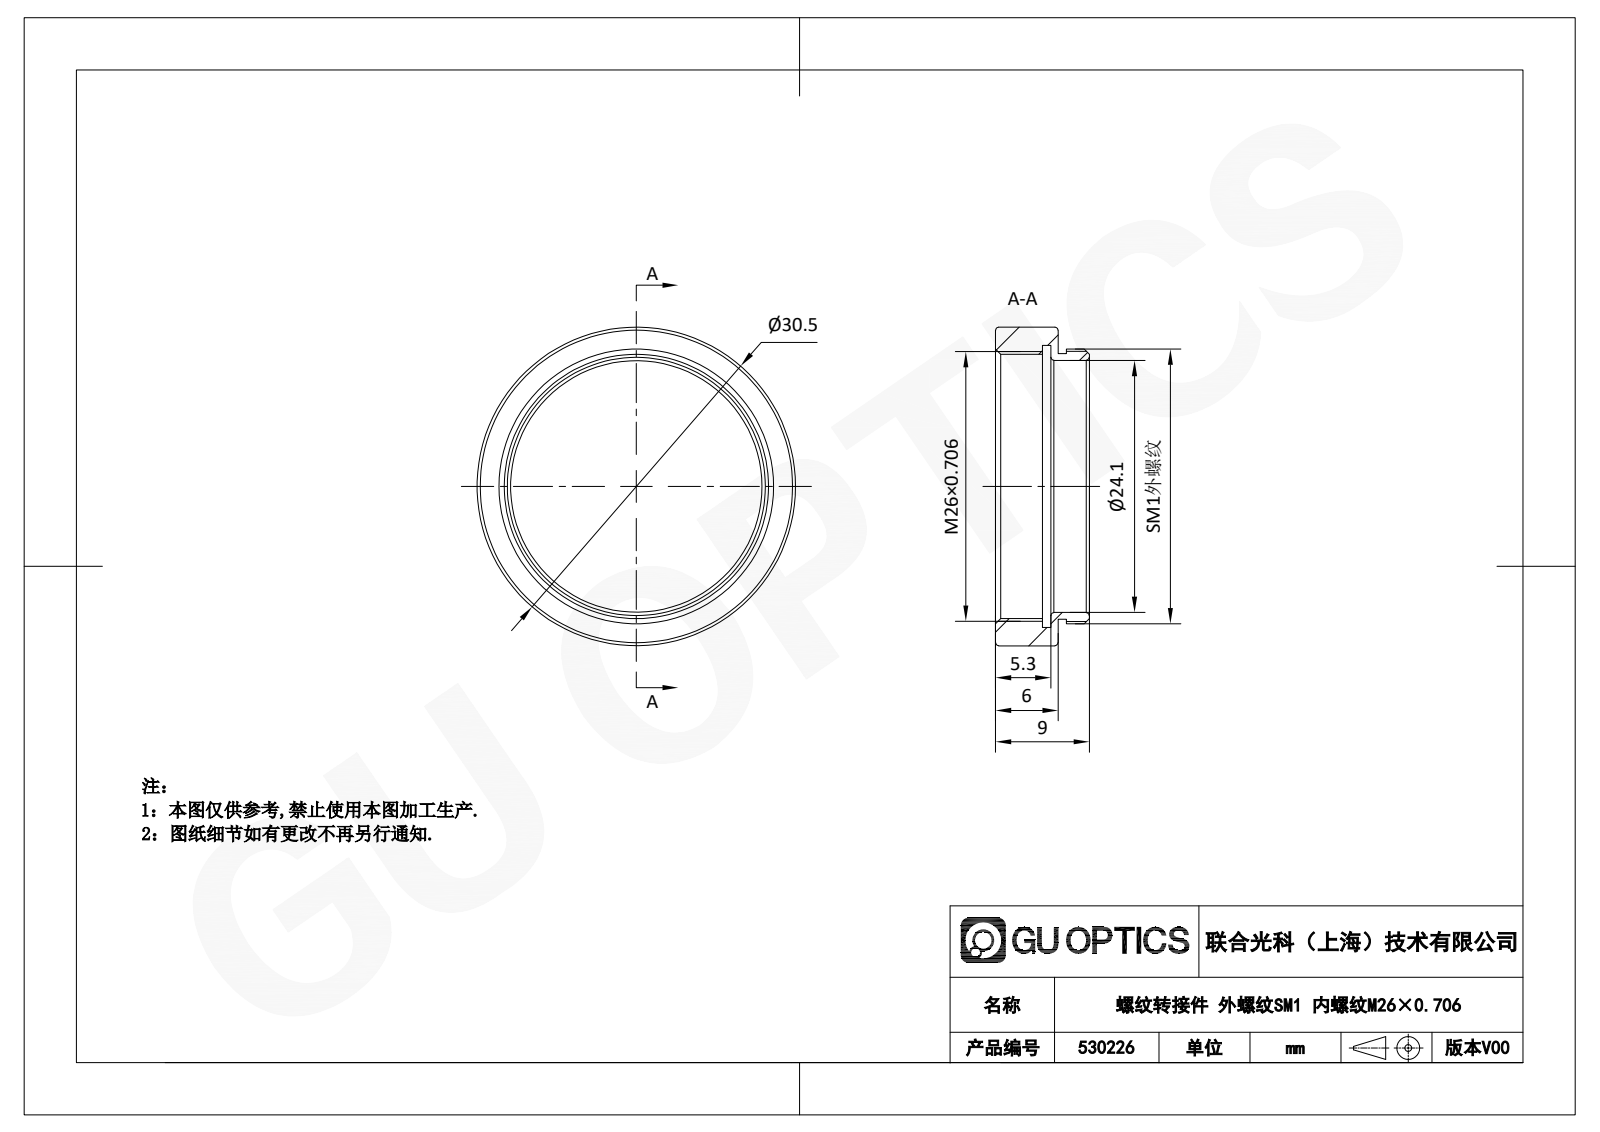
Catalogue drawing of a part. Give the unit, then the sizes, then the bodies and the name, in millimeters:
Units: millimetres
Overall size (bounding box): 30.5 × 30.5 × 9
Round holes (diameter × count): ⌀24.1 ×1, ⌀25.3 ×1, ⌀27 ×1
Round bosses / shafts (diameter × count): ⌀30.5 ×1, ⌀26.29 ×1, ⌀25.4 ×1
Main face-to-face distances: 6, 0.8, 1.5, 4.5, 0.7, 5.3, 2.3, 6.8, 2.2, 3
Volume: 1 548 mm³ · Surface area: 2 195 mm²
Bodies: 1 solid, 18 faces (6 planar, 6 cylindrical, 6 other)
Part name (STEP PRODUCT): 530226
STEP written by: SolidWorks 2020 (CONFIG_CONTROL_DESIGN)
